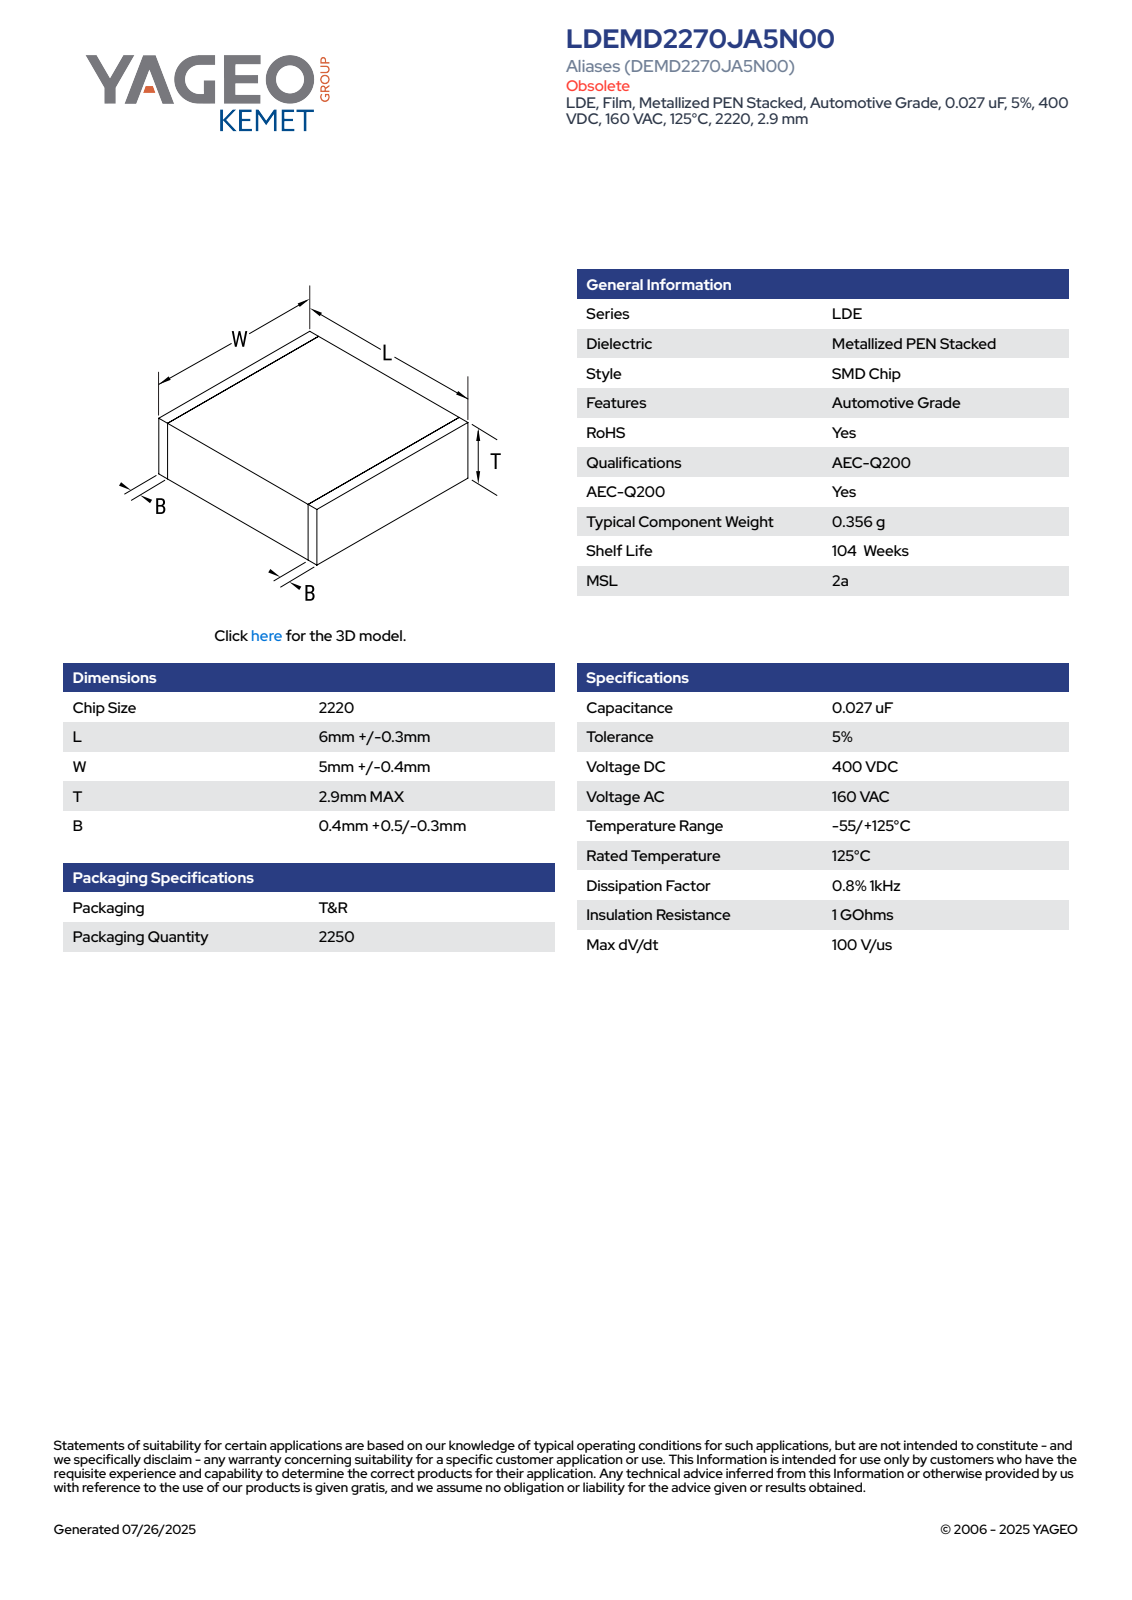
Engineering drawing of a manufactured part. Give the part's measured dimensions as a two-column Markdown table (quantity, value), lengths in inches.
| quantity | value |
| --- | --- |
| part name | CFS_LDELDB_2220_L6.3W5.4T2.9B0.9 |
| STEP written by | SolidWorks 2020 (AUTOMOTIVE_DESIGN) |
| units | inches |
| bodies | 4 solids, 73 faces (73 planar, 0 cylindrical, 0 other) |
| overall size | 0.248 × 0.213 × 0.114 |
| volume | 0.006 in³ |
| surface area | 0.214 in² |
| main face-to-face distances | 0.113, 0.248, 0.212, 0.114, 0.212, 0.114, 0.213, 0.02, 0.228, 0.209 |
